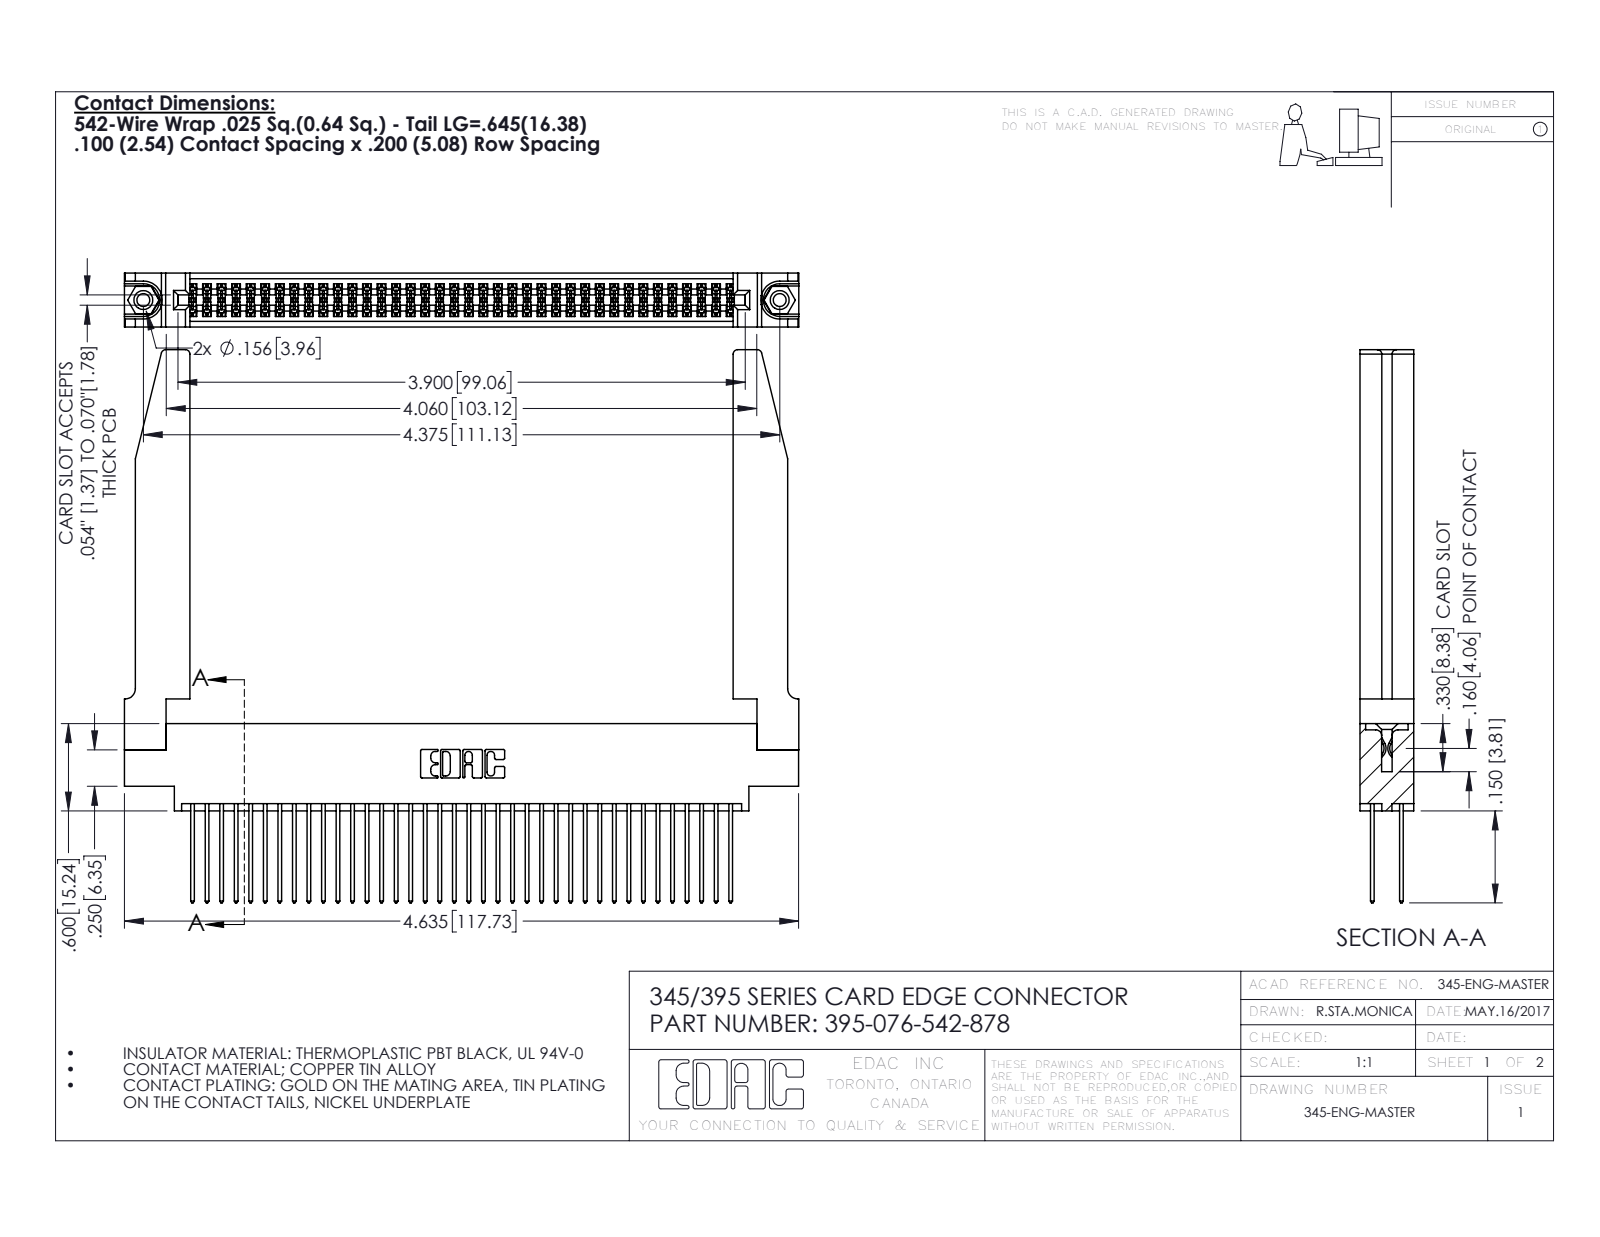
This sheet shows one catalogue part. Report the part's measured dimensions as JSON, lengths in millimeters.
{"part_name": "345-292-001_345-293-142; 345 Part_0.170 Offset - 0.156 Dia-TH; 345-220-078_345-220-078; 395-076-542-878 (+1 more)", "step_written_by": "SolidWorks 2016 (CONFIG_CONTROL_DESIGN)", "units": "millimeters", "bodies": {"solids": 81, "faces": 4164, "planar": 2734, "cylindrical": 1378, "other": 52}, "overall_size": [117.8, 96.6, 9.4], "volume_mm3": 19420, "surface_area_mm2": 25770, "round_holes": [[2.3, 2], [3.2, 2], [4, 2], [1.6, 1]], "round_bosses_or_shafts": [[3.9, 2]], "partial_cylinders_radius": [[0.2, 114], [0.3, 76], [0.3, 22], [0.8, 8], [0.2, 6], [0.8, 6], [0.7, 3], [0.4, 2]], "face_to_face_distances": [1.8, 7.6, 9.4, 2.5, 6.9, 0.6, 5.1, 5.7, 4.4, 3.8], "hole_center_spacings": [6.9, 105.1, 111.1]}
